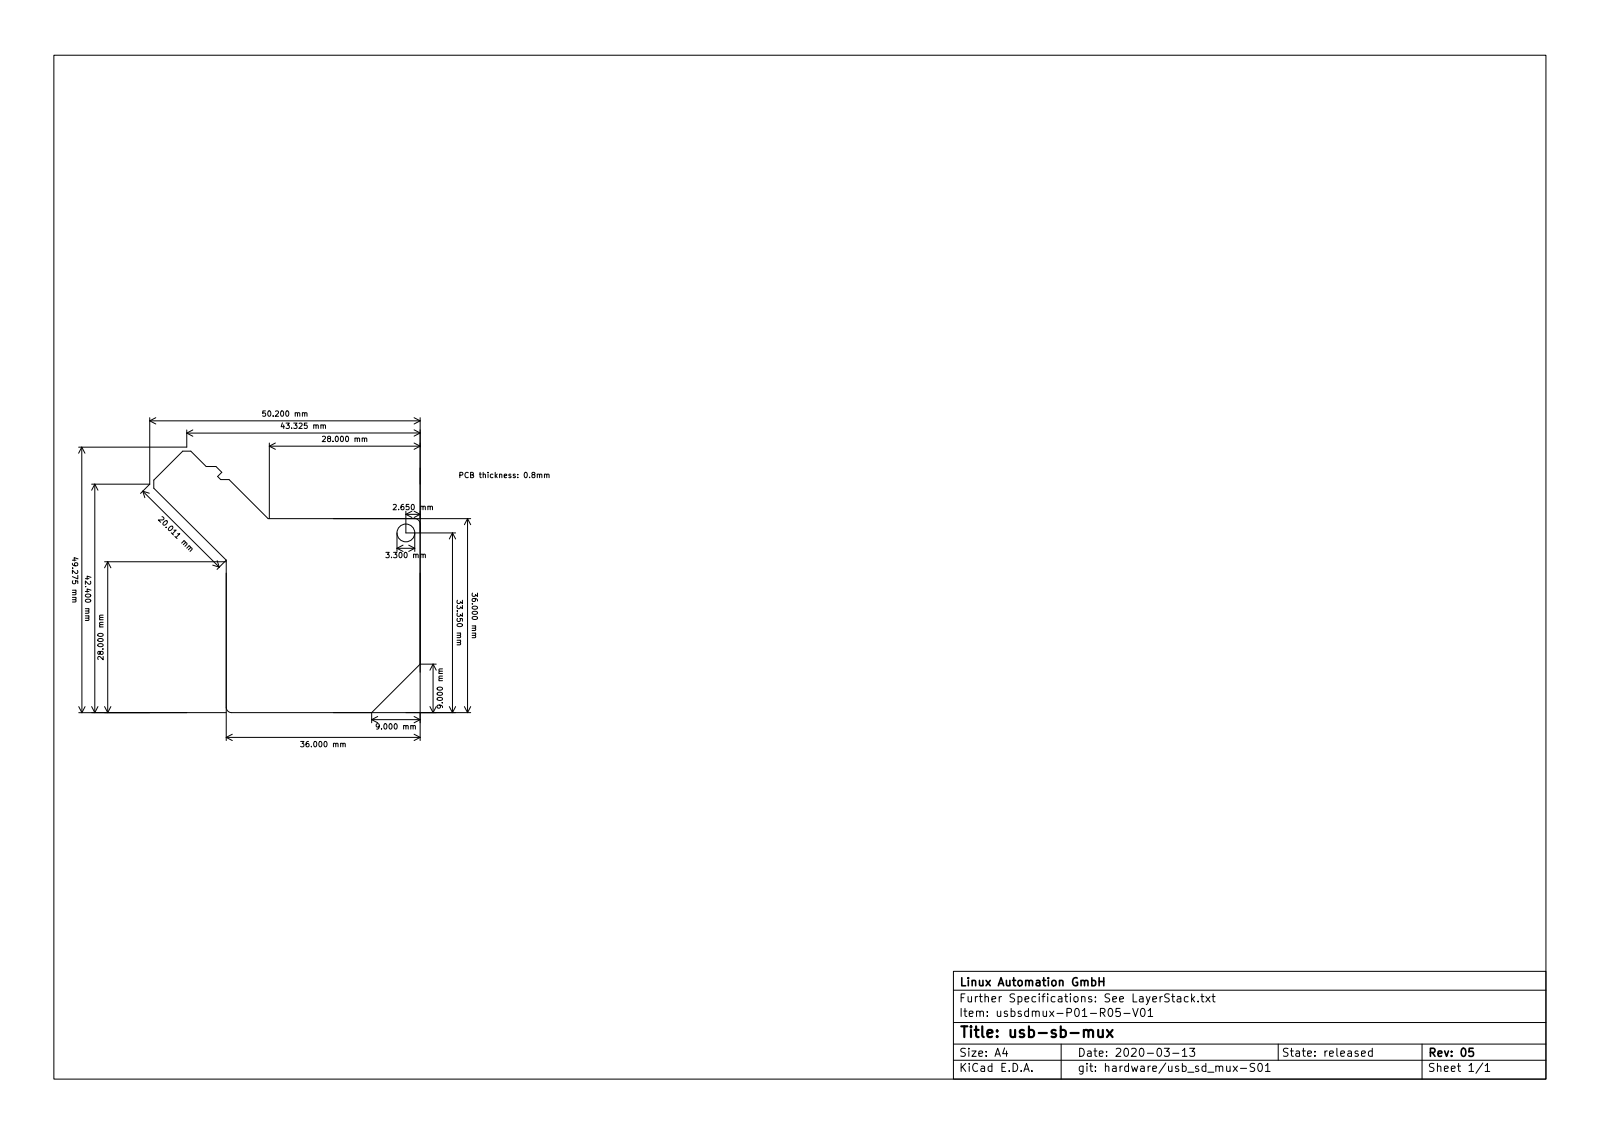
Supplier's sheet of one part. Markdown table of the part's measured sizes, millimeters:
| quantity | value |
| --- | --- |
| part name | usb-sd-mux; Board_Geoms_d9eb; Local_CS_d9eb; Pcb_d9eb (+8 more) |
| STEP written by | FreeCAD (AUTOMOTIVE_DESIGN) |
| units | millimeters |
| bodies | 139 solids, 3271 faces (2432 planar, 809 cylindrical, 30 other) |
| overall size | 49.45 × 48.52 × 5.25 |
| volume | 1 910 mm³ |
| surface area | 6 077 mm² |
| round holes (diameter × count) | 0.3 × 14, 0.4 × 2, 1 × 1, 3.3 × 1 |
| partial cylindrical surfaces (radius × count) | 0.1 × 85, 0.2 × 82, 0.4 × 27, 0.3 × 24, 0.25 × 23, 0.5 × 9, 0.6 × 8, 0.15 × 6 |
| main face-to-face distances | 0.8, 2.47, 1.68, 1.67, 0.79, 1.29, 1.44, 1.52, 1.53, 2.32 |
| hole center spacings | 1, 0.9, 1.27, 2, 2.24, 2.83, 1.41, 1.42 |
